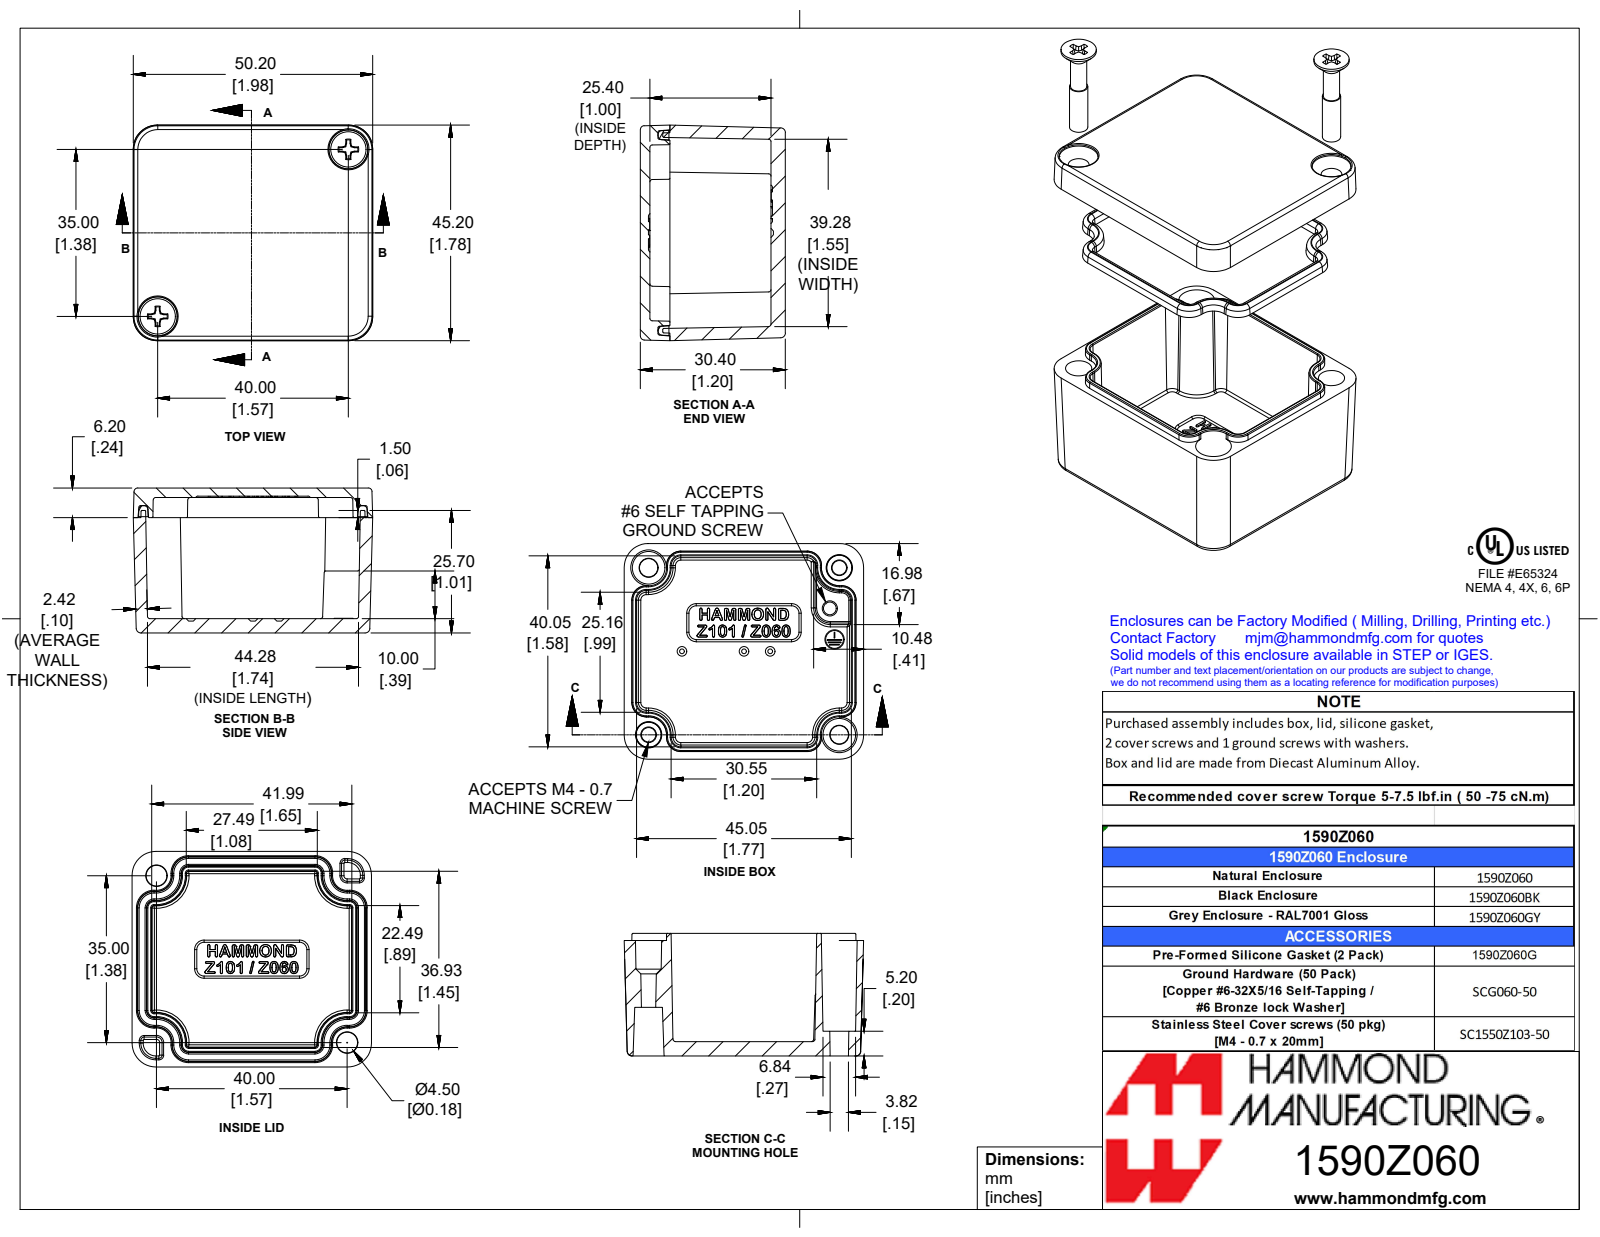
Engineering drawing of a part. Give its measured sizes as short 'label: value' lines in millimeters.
name: 1590Z060
written by: SolidWorks 2019 (CONFIG_CONTROL_DESIGN)
unit: mm
bodies: 4 solids, 1051 faces (333 planar, 158 cylindrical, 560 other)
size: 50.2 × 45.2 × 30.4
volume: 24 830 mm³; area: 21 740 mm²
bosses: 2× ⌀3.8, 2× ⌀3.4
rounds: 40× R0.2, 34× R0.5, 22× R0.3, 8× R5, 4× R0.8, 4× R1
face distances: 30.4, 3, 2, 27.4, 28.4, 25.4, 4.2, 24.2, 21.2, 6.2
